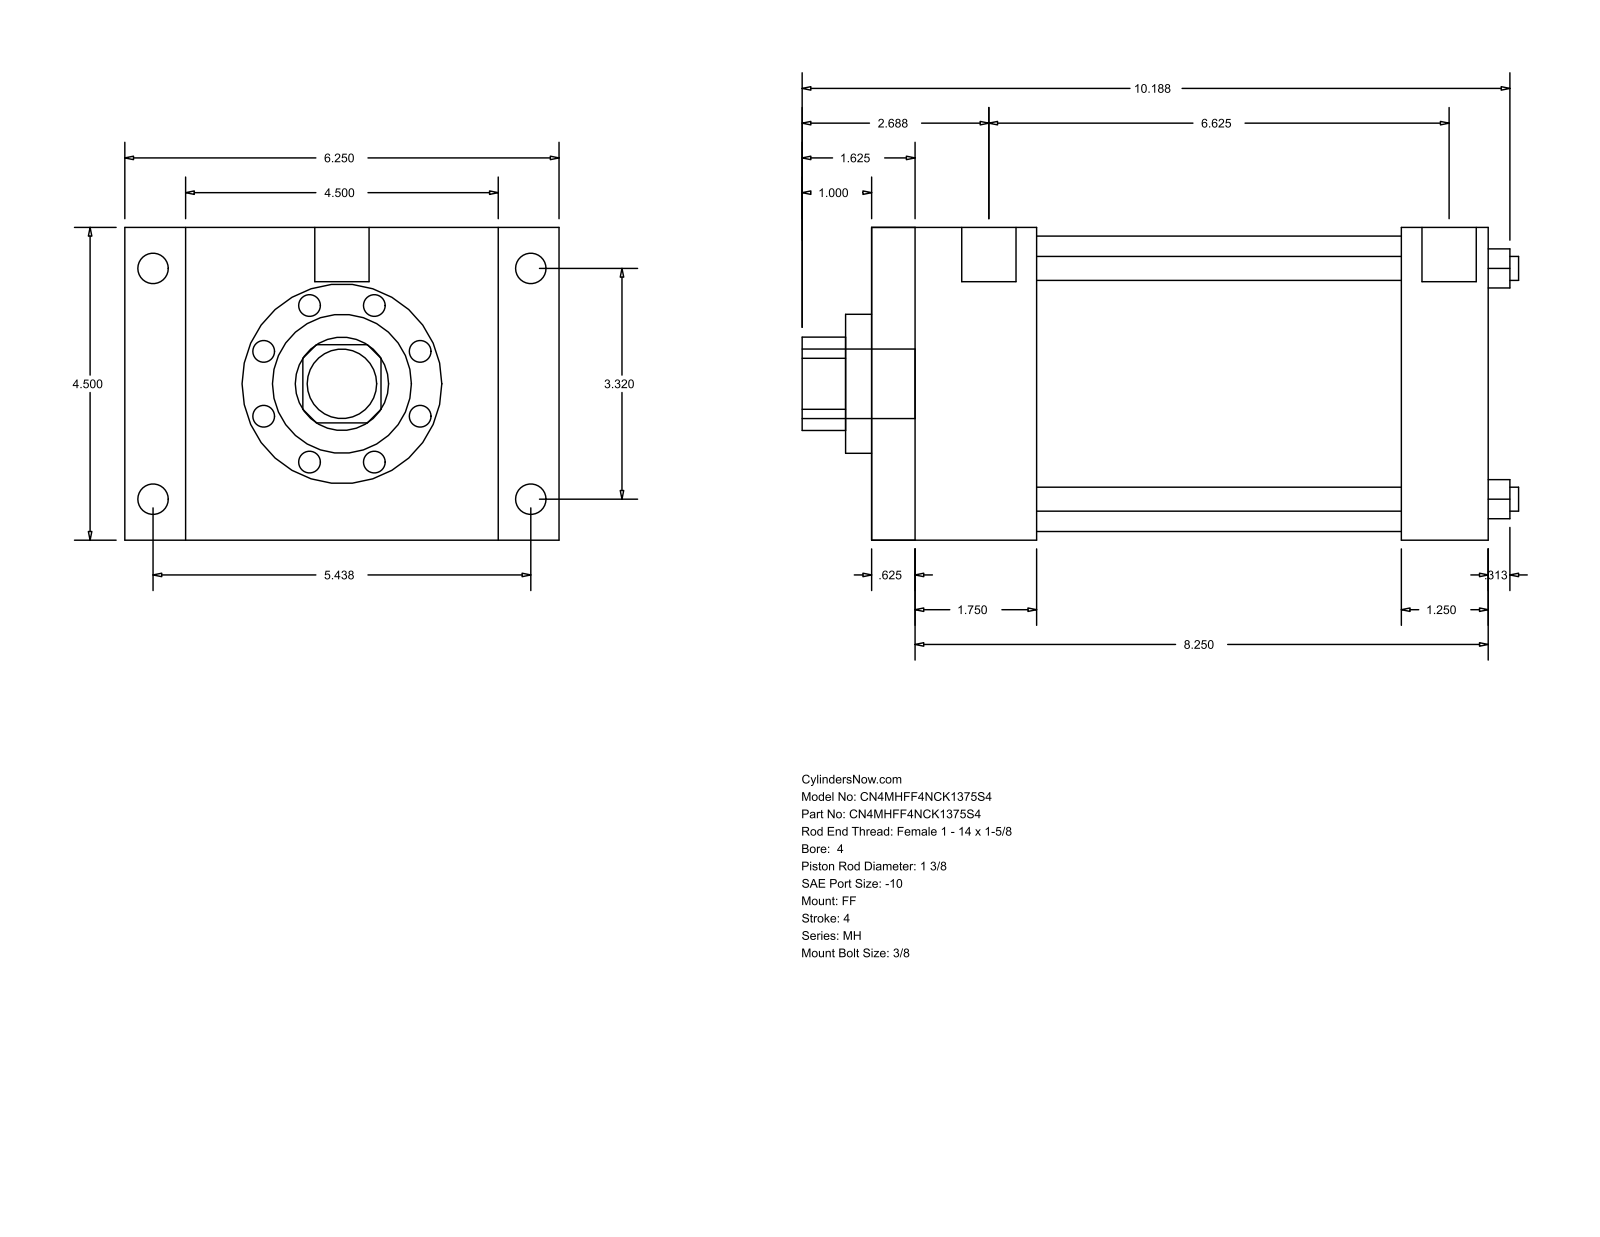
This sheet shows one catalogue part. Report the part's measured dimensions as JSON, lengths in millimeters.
{"part_name": "MH_FF__0400_1.375", "step_written_by": "GSSL Pune (CONFIG_CONTROL_DESIGN)", "units": "millimeters", "bodies": {"solids": 0, "faces": 92, "planar": 64, "cylindrical": 28, "other": 0}, "overall_size": [261.94, 158.75, 114.3], "round_holes": [[8.76, 4], [34.92, 1], [50.8, 1], [107.95, 1]], "round_bosses_or_shafts": [[11.13, 4], [8.73, 4], [19.84, 2], [25.4, 1]], "partial_cylinders_radius": [[17.06, 1]], "face_to_face_distances": [114.3, 225.42, 15.87, 209.55, 60.32, 44.45, 165.1, 193.67, 177.8, 133.35], "hole_center_spacings": [59.62, 84.32, 119.25]}
